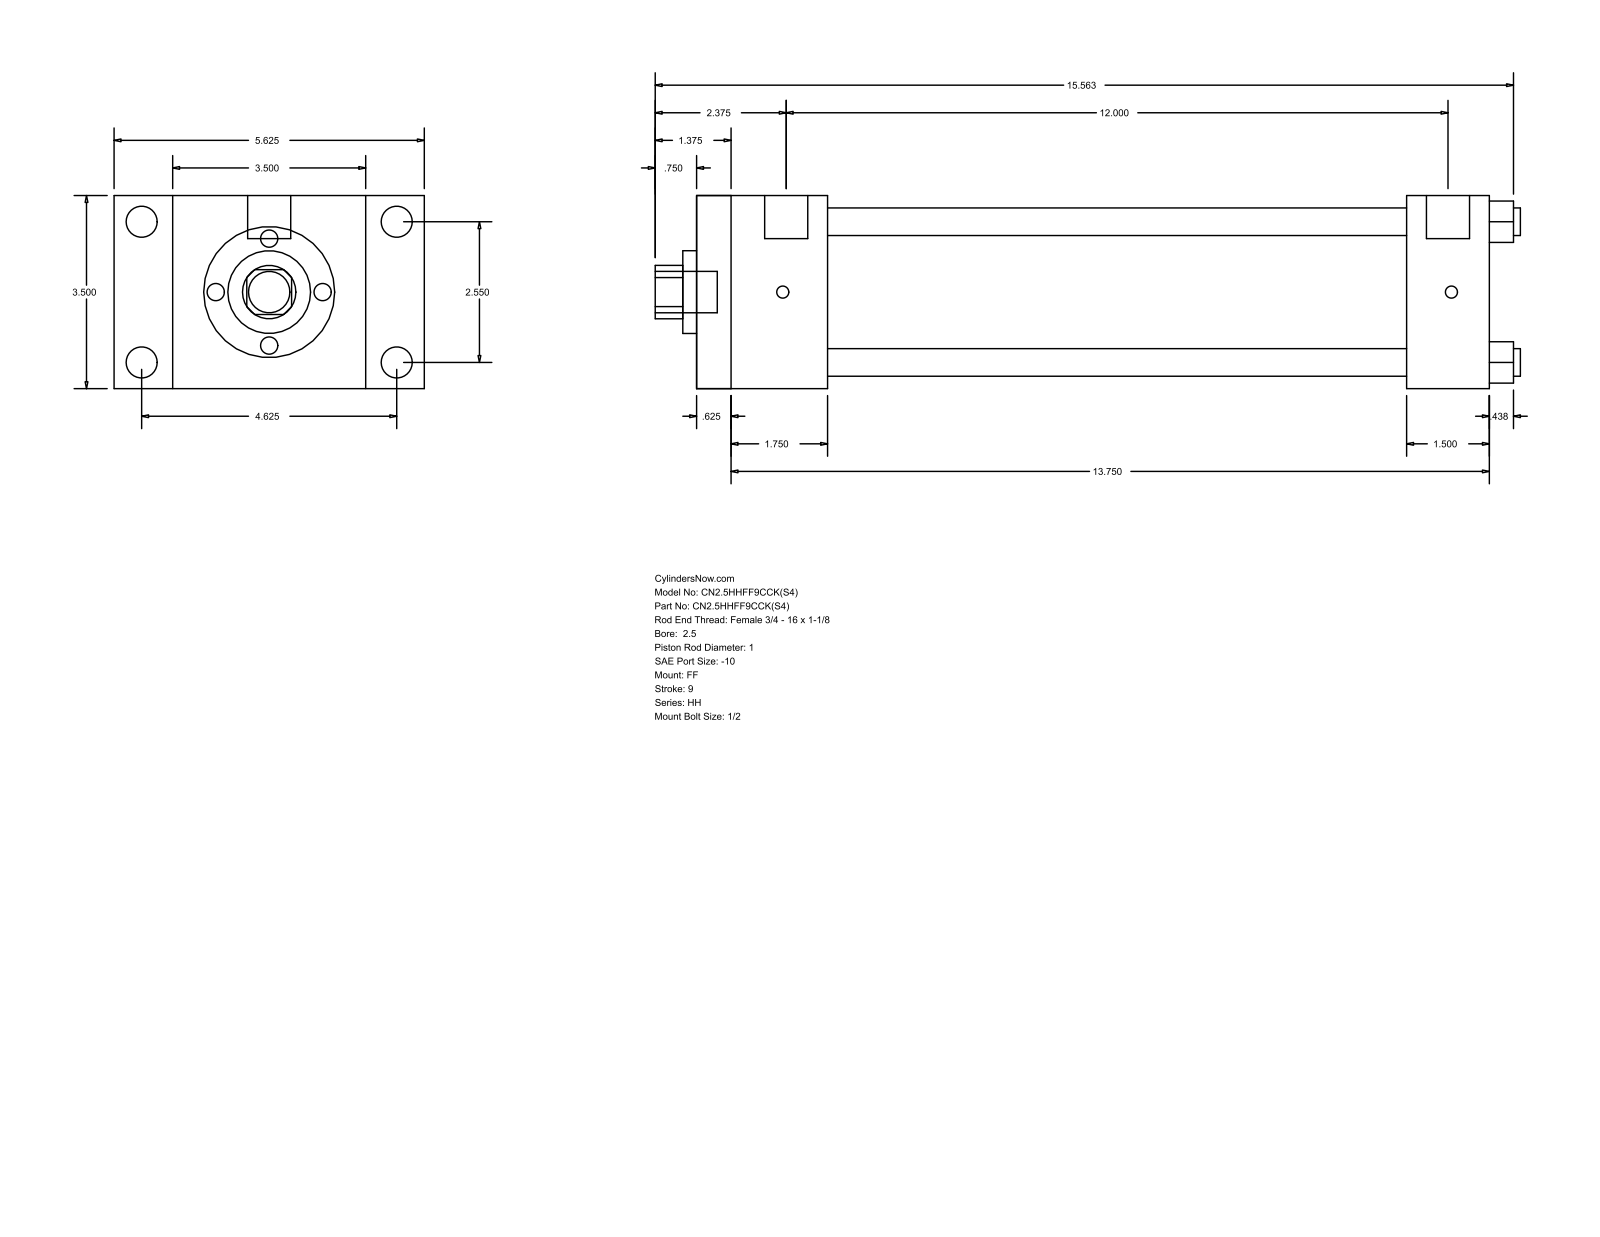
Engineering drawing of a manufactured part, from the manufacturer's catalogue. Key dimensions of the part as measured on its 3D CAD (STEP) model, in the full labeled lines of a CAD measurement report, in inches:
Part name (STEP PRODUCT): HH_FF__0250_1
STEP written by: GSSL Pune (CONFIG_CONTROL_DESIGN)
Units: inches
Bodies: 0 solids, 92 faces (64 planar, 28 cylindrical, 0 other)
Overall size (bounding box): 15.687 × 5.625 × 3.5
Round holes (diameter × count): ⌀0.5 ×4, ⌀1 ×1, ⌀1.5 ×1, ⌀2.875 ×1
Round bosses / shafts (diameter × count): ⌀0.563 ×4, ⌀0.219 ×4, ⌀0.781 ×2, ⌀0.75 ×1
Partial cylindrical surfaces — rounded edges, fillets, slot ends (radius × count): R0.484 ×1
Main face-to-face distances: 3.5, 14.375, 0.625, 13.75, 2.375, 1.75, 12, 12.875, 12.25, 10.5
Hole centre spacings: 1.803, 2.55, 3.606
